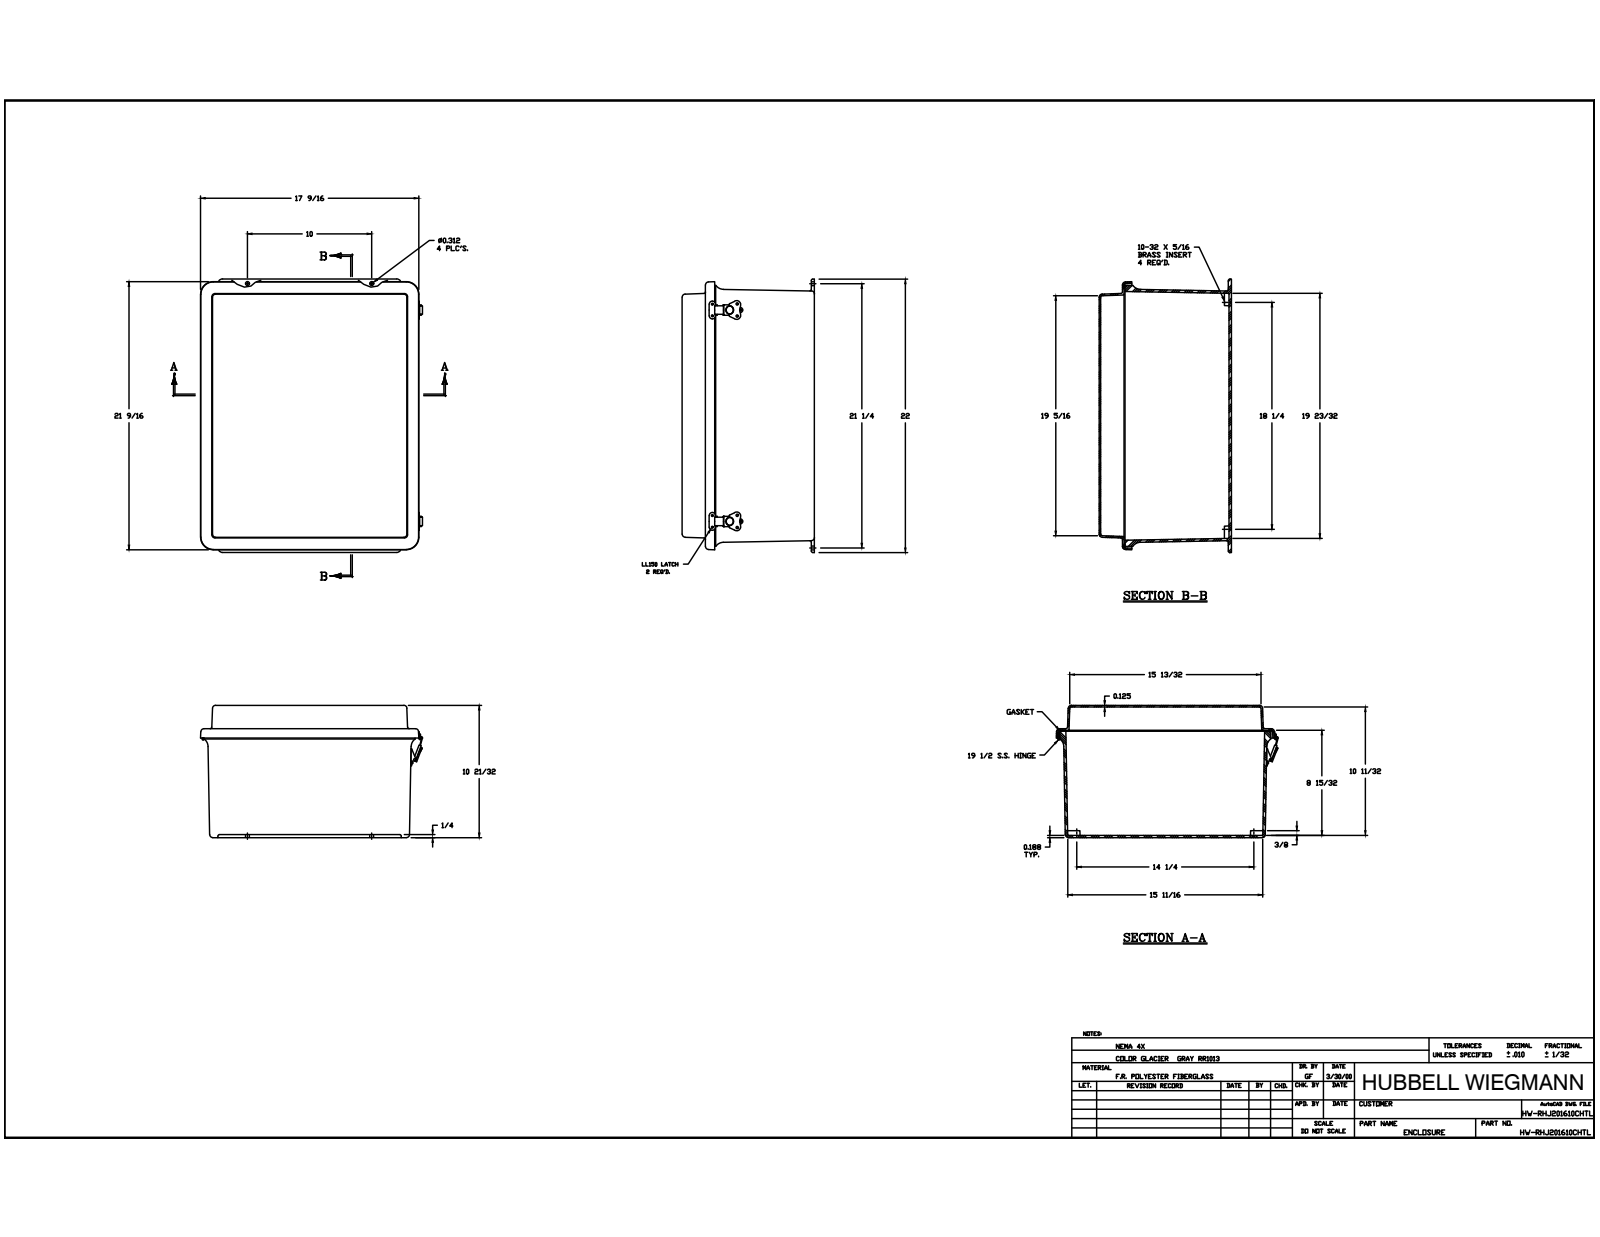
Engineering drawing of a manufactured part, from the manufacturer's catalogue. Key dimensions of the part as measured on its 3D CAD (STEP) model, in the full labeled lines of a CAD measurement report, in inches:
Part name (STEP PRODUCT): J2016HL; RMINS45821P; RMINS45821P_1; RMINS45821P_2 (+8 more)
STEP written by: Autodesk Inventor 2014 (AUTOMOTIVE_DESIGN)
Units: inches
Bodies: 52 solids, 1365 faces (653 planar, 513 cylindrical, 199 other)
Overall size (bounding box): 22 × 17.753 × 10.642
Volume: 270.5 in³ · Surface area: 3 193 in²
Round holes (diameter × count): ⌀0.104 ×20, ⌀0.14 ×20, ⌀0.131 ×12, ⌀0.152 ×5, ⌀0.13 ×4, ⌀0.156 ×4, ⌀0.165 ×4, ⌀0.197 ×4, ⌀0.218 ×4, ⌀0.118 ×2, ⌀0.138 ×2, ⌀0.181 ×2
Round bosses / shafts (diameter × count): ⌀0.14 ×20, ⌀0.27 ×4, ⌀0.583 ×2, ⌀0.524 ×2, ⌀0.209 ×2, ⌀0.185 ×2, ⌀0.128 ×2, ⌀0.155 ×1
Partial cylindrical surfaces — rounded edges, fillets, slot ends (radius × count): R0.125 ×22, R0.079 ×19, R0.25 ×12, R0.039 ×8, R0.045 ×8, R0.047 ×8, R0.086 ×8, R0.093 ×8
Main face-to-face distances: 0.187, 0.125, 0.188, 10.517, 10.642, 10.329, 10.454, 2, 8.642, 8.454
Hole centre spacings: 3.75, 7.5, 17, 11, 11.5, 7.25, 7.75, 0.945
